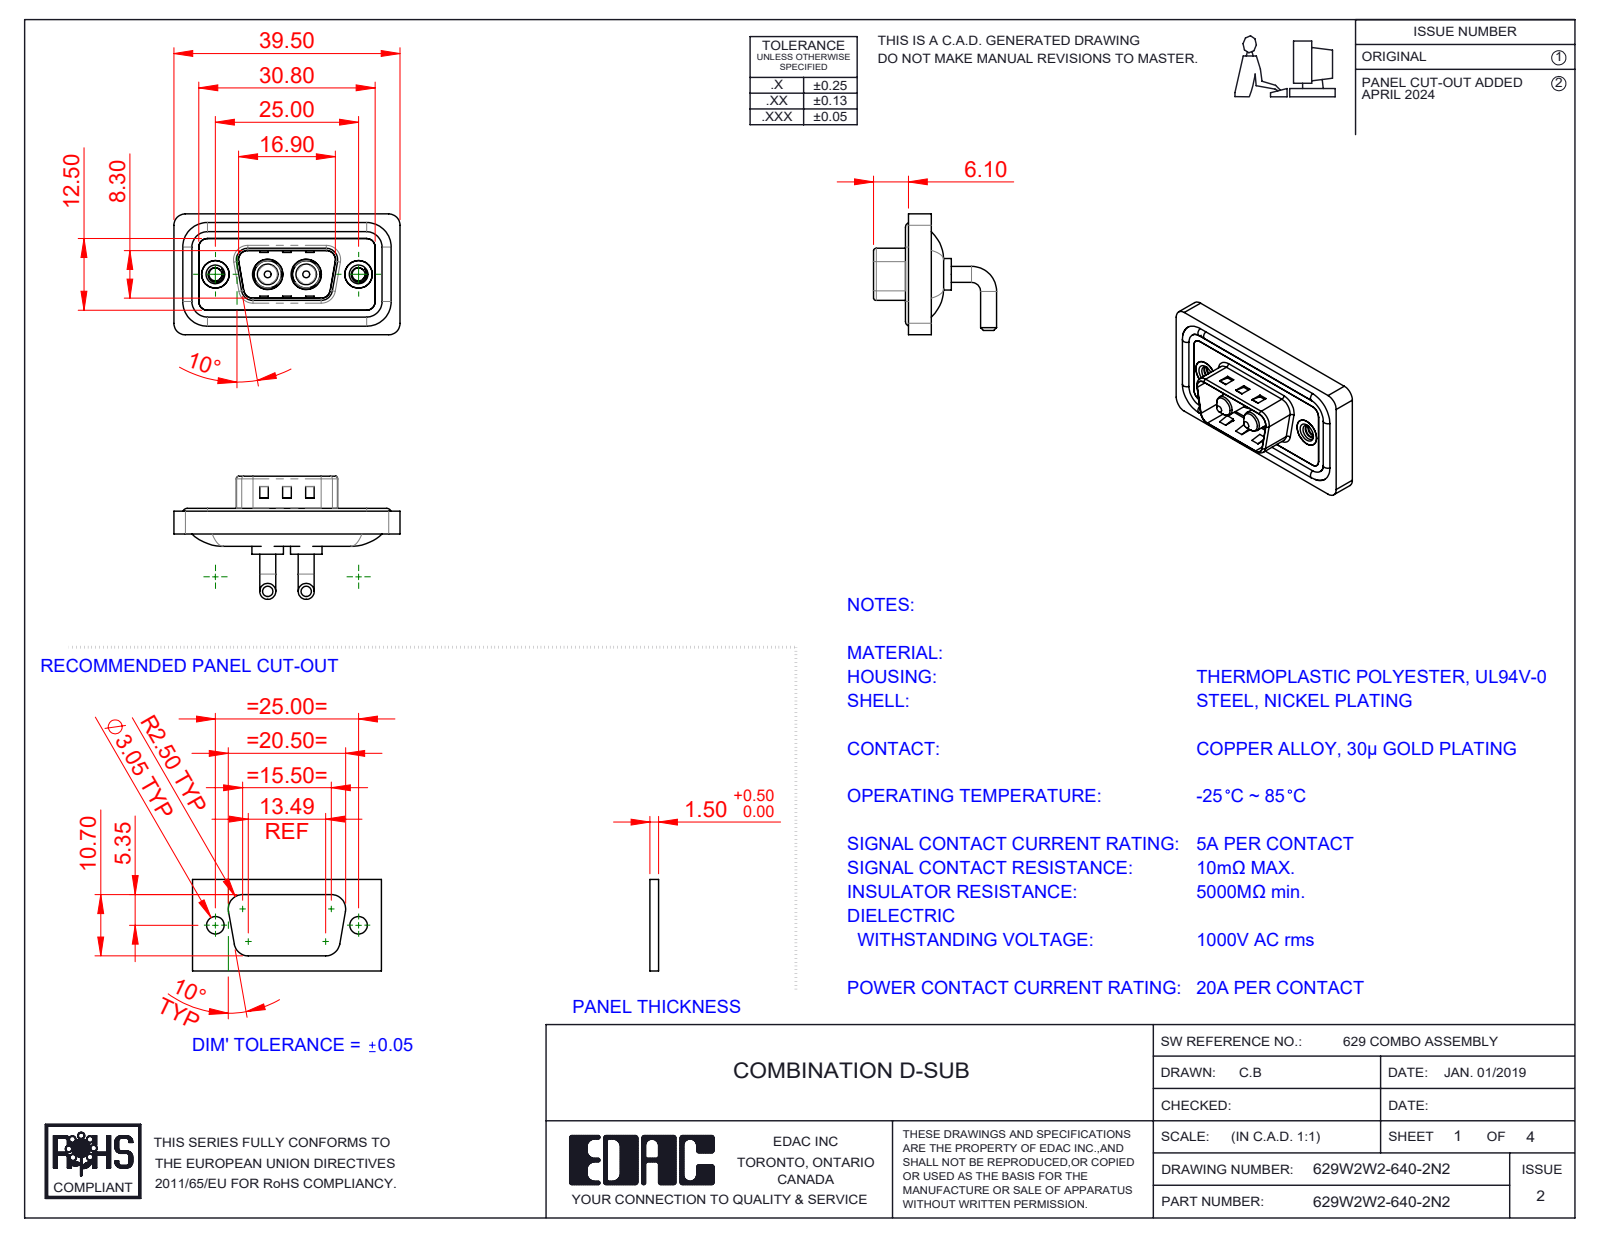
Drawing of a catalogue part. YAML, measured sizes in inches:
part_name: "Power Pin_20A RA; 629Combo Shell Rear_09 Contacts; 629Combo Threaded Rivet_2; 629Combo Housing_2W2 (+3 more)"
step_written_by: "SolidWorks 2023 (CONFIG_CONTROL_DESIGN)"
units: inches
bodies: {solids: 11, faces: 497, planar: 165, cylindrical: 222, other: 110}
overall_size: [1.555, 0.846, 0.831]
volume: 0.28
surface_area: 11.11
round_holes:
  - {diameter: 0.089, count: 2}
  - {diameter: 0.157, count: 2}
  - {diameter: 0.189, count: 2}
  - {diameter: 0.191, count: 2}
  - {diameter: 0.197, count: 2}
  - {diameter: 0.209, count: 2}
round_bosses_or_shafts:
  - {diameter: 0.11, count: 4}
  - {diameter: 0.063, count: 4}
  - {diameter: 0.217, count: 2}
  - {diameter: 0.205, count: 2}
  - {diameter: 0.193, count: 2}
  - {diameter: 0.187, count: 2}
  - {diameter: 0.148, count: 2}
  - {diameter: 0.142, count: 2}
partial_cylinders:
  - {radius: 0.059, count: 18}
  - {radius: 0.079, count: 18}
  - {radius: 0.02, count: 8}
  - {radius: 0.063, count: 8}
  - {radius: 0.01, count: 4}
  - {radius: 0.024, count: 4}
  - {radius: 0.026, count: 4}
  - {radius: 0.035, count: 4}
face_to_face_distances: [0.016, 0.114, 0.043, 0.031, 0.083, 0.098, 0.122, 0.063, 0.177, 0.059]
hole_center_spacings: [0.36, 0.624, 0.265, 0.984]
